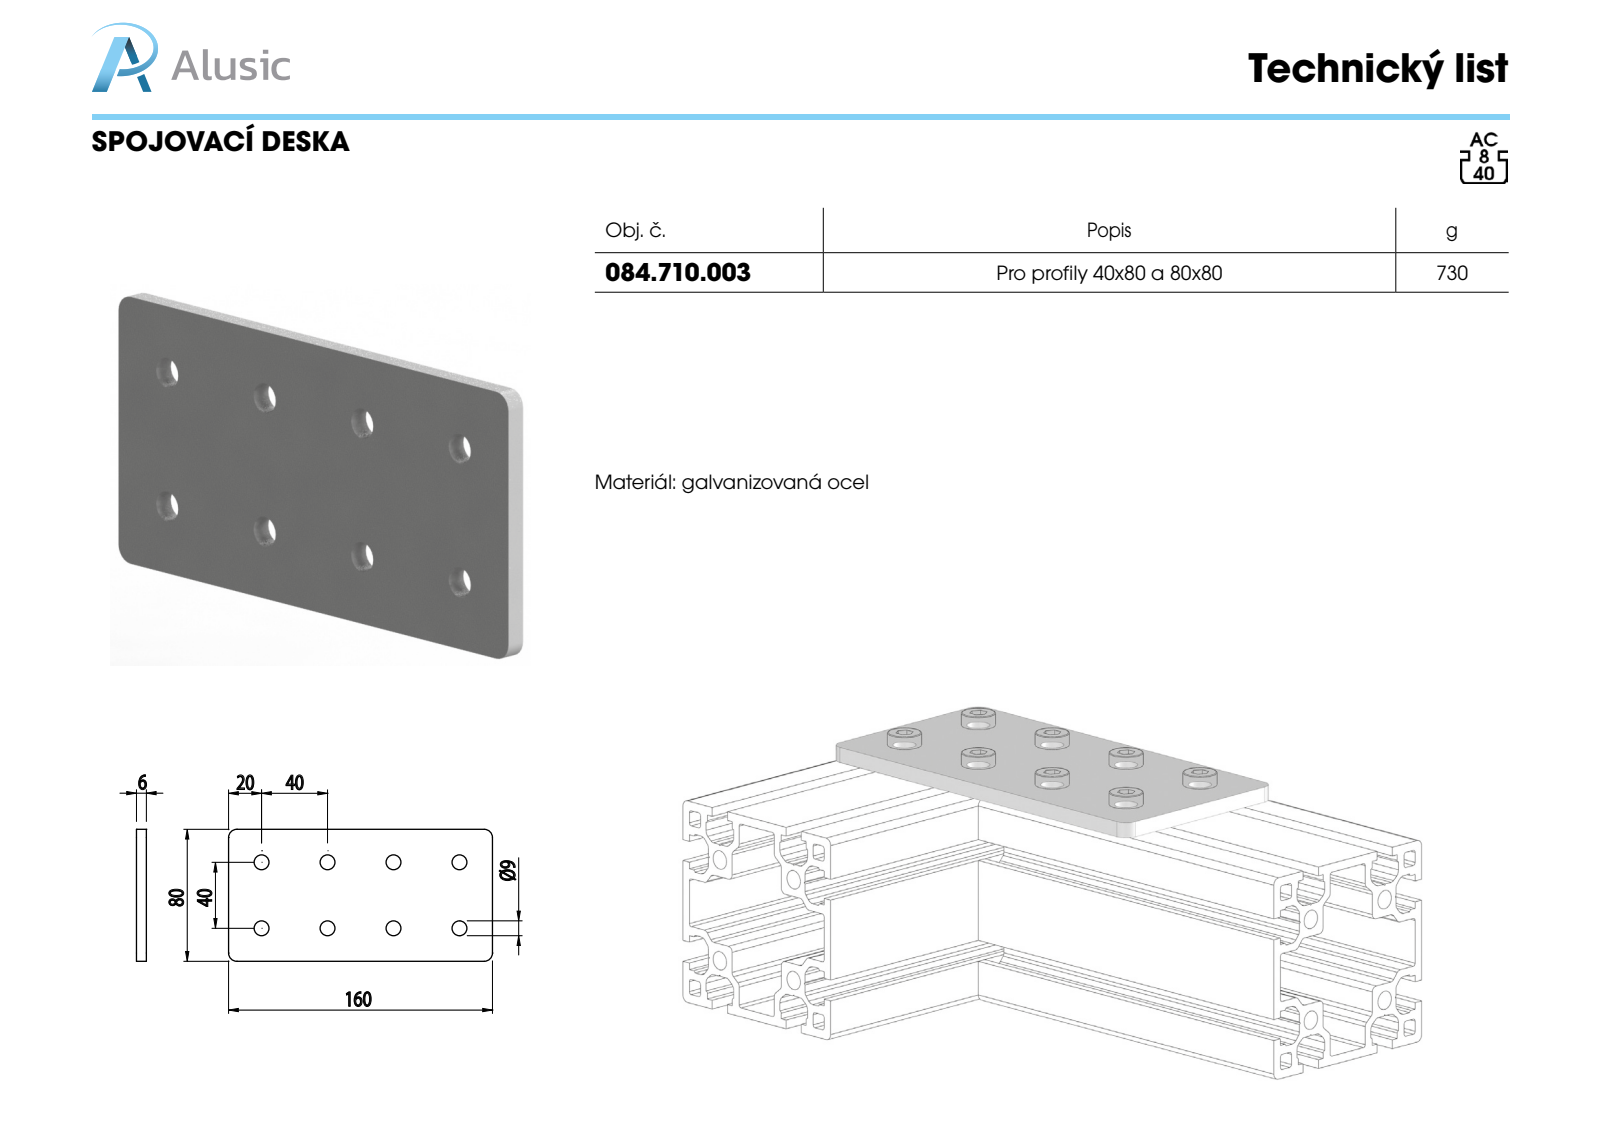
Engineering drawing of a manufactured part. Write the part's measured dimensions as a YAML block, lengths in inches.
part_name: "084.710.003"
step_written_by: "SolidWorks 2011 (CONFIG_CONTROL_DESIGN)"
units: inches
bodies: {solids: 1, faces: 26, planar: 6, cylindrical: 20, other: 0}
overall_size: [6.299, 3.15, 0.236]
volume: 4.492
surface_area: 44.52
round_holes:
  - {diameter: 0.354, count: 8}
partial_cylinders:
  - {radius: 0.197, count: 4}
face_to_face_distances: [0.236, 3.15, 6.299]
hole_center_spacings: [1.575, 2.227, 3.15, 3.521, 4.724, 4.98]
